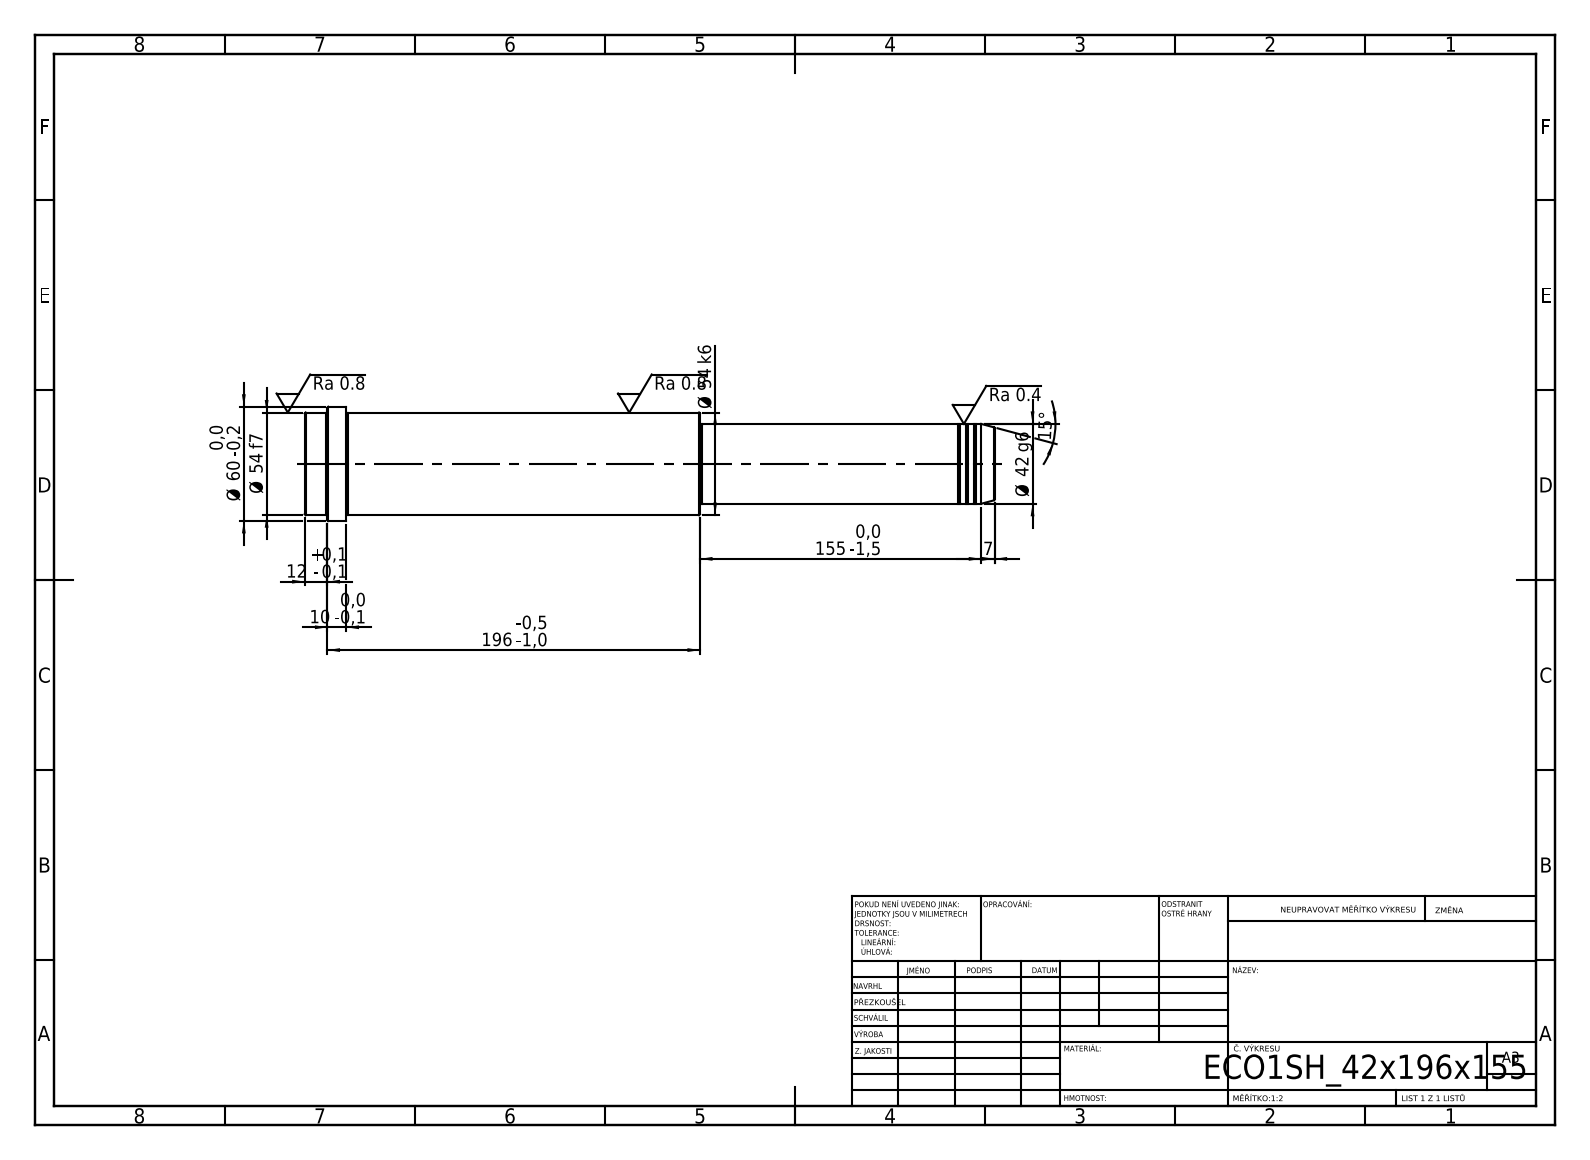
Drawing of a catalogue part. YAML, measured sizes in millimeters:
step_written_by: "SolidWorks 2019 (CONFIG_CONTROL_DESIGN)"
units: millimeters
bodies: {solids: 1, faces: 52, planar: 6, cylindrical: 16, other: 30}
overall_size: [363, 60, 60]
volume: 695221
surface_area: 61697
round_bosses_or_shafts:
  - {diameter: 60, count: 1}
  - {diameter: 54, count: 1}
  - {diameter: 42, count: 1}
  - {diameter: 41, count: 1}
face_to_face_distances: [363, 155, 208, 341, 186, 22, 351, 196, 10, 12]
